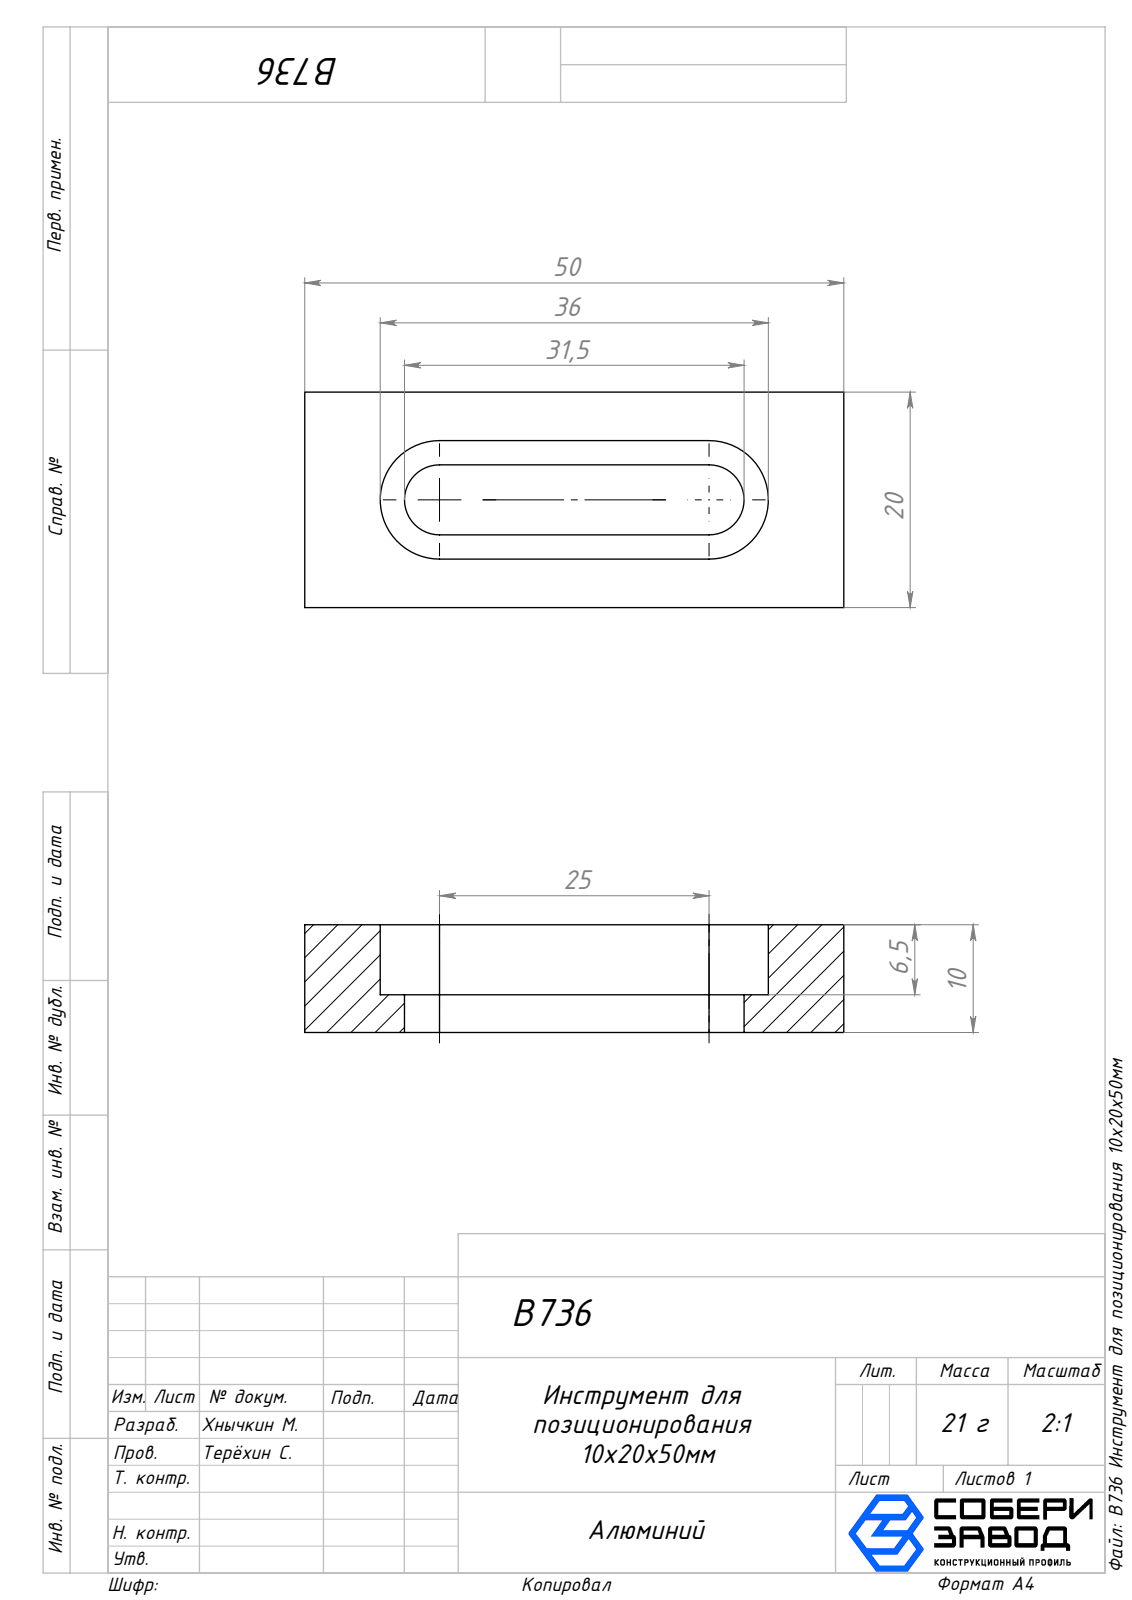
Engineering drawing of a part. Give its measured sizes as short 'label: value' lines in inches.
name: B736 Инструмент для позиционирования 10x20x50мм
written by: SolidWorks 2025 (AUTOMOTIVE_DESIGN)
unit: in
bodies: 1 solid, 15 faces (11 planar, 4 cylindrical, 0 other)
size: 1.969 × 0.787 × 0.394
volume: 0.422 in³; area: 5.898 in²
rounds: 2× R0.128, 2× R0.217
face distances: 0.394, 0.787, 0.177, 0.61, 0.256, 1.969, 0.266, 0.522, 0.089, 0.344
